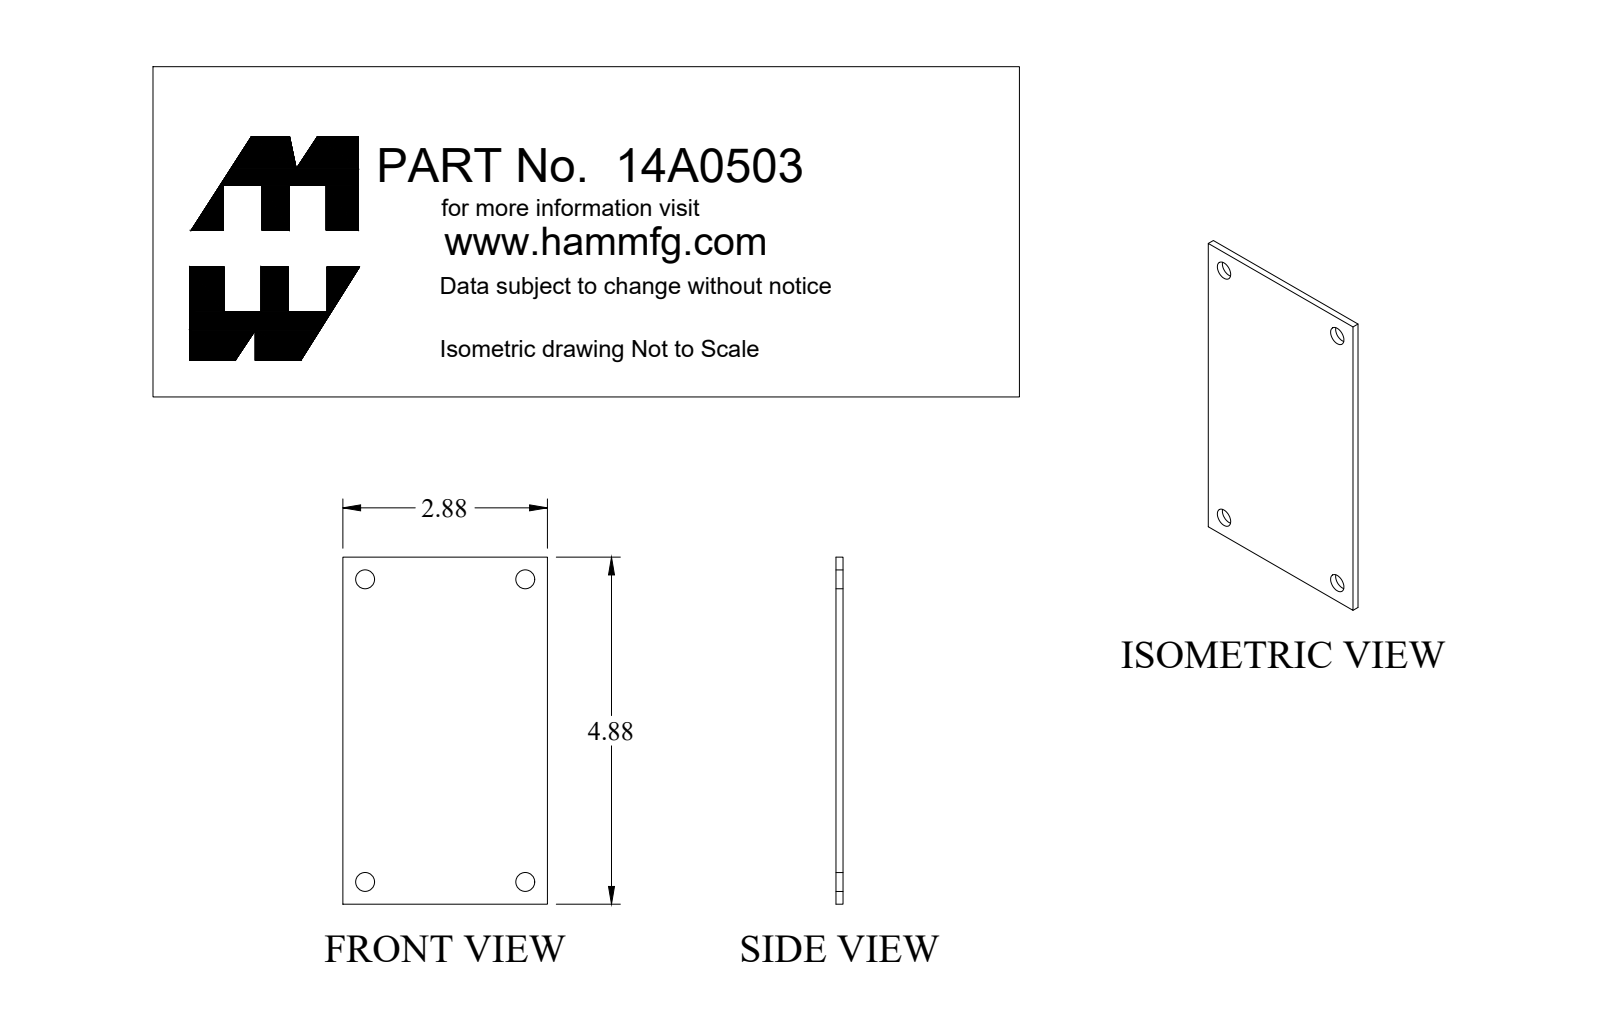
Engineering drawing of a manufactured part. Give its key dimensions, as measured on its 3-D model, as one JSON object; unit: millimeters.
{"part_name": "14A0503", "step_written_by": "SolidWorks 2018 (AUTOMOTIVE_DESIGN)", "units": "millimeters", "bodies": {"solids": 1, "faces": 10, "planar": 6, "cylindrical": 4, "other": 0}, "overall_size": [123.8, 73, 2.5], "volume_mm3": 22610, "surface_area_mm2": 19010, "round_holes": [[6.7, 2], [6.7, 2]], "face_to_face_distances": [2.5, 73, 123.8], "hole_center_spacings": [57.2, 108, 122.2]}
